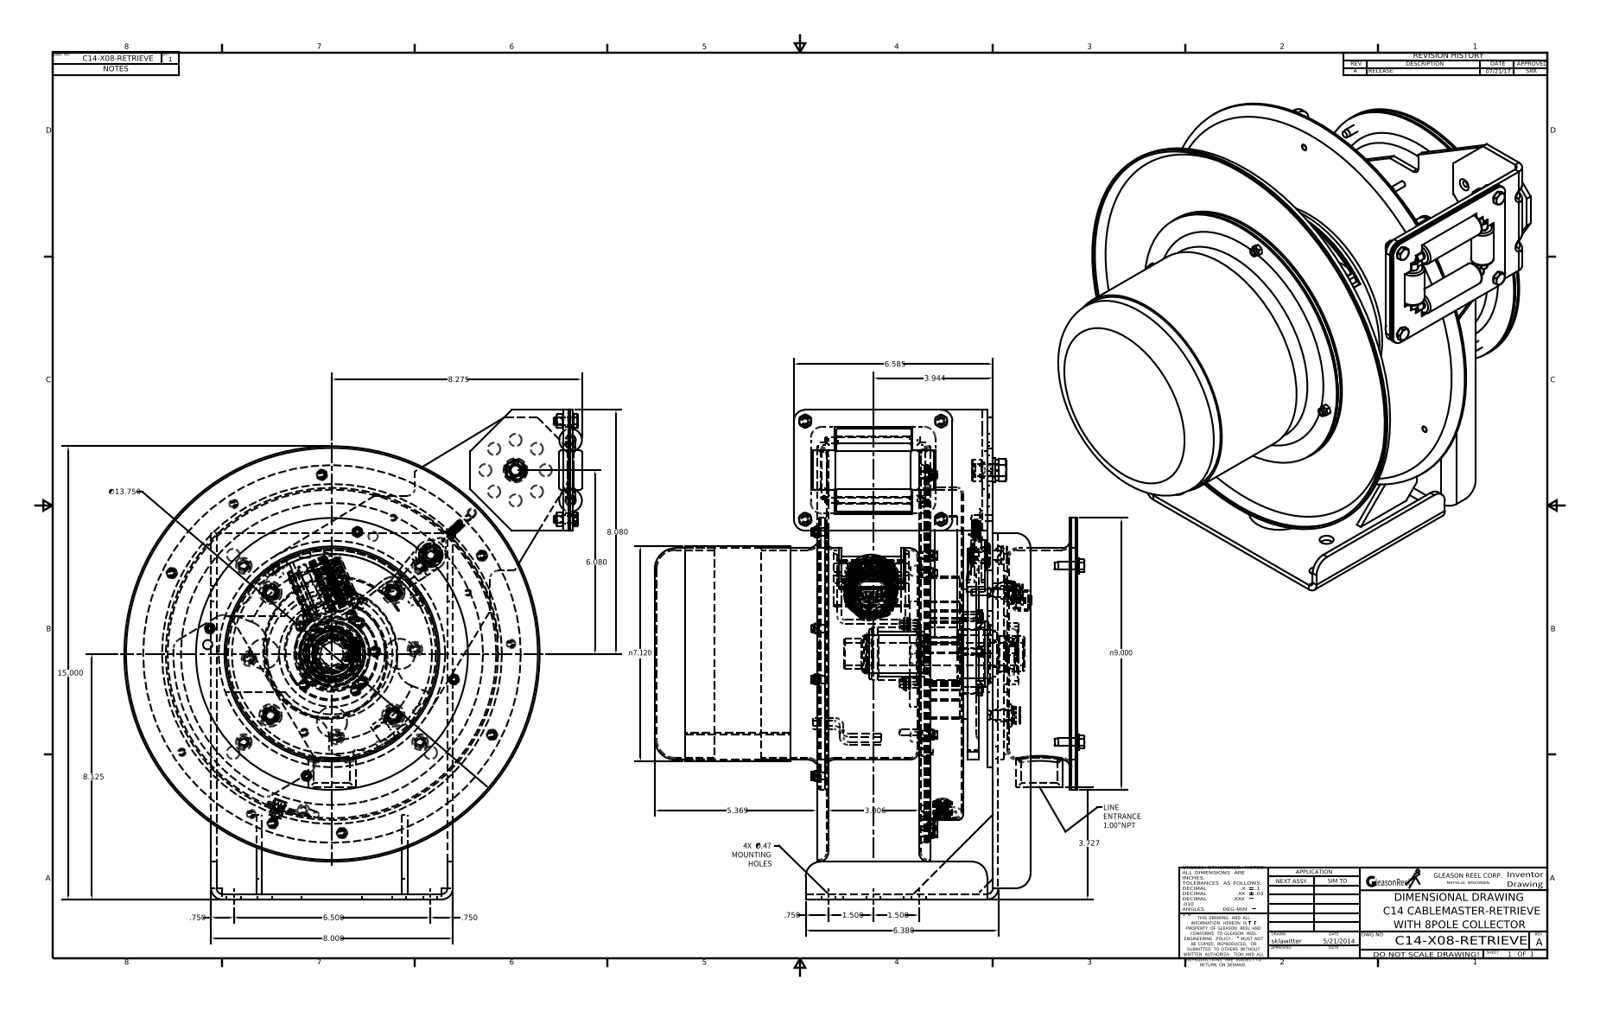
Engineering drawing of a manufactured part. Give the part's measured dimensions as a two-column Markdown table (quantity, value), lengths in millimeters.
| quantity | value |
| --- | --- |
| part name | C14-X08-RETRIEVE (SW) |
| STEP written by | Autodesk Inventor 2016 (AUTOMOTIVE_DESIGN) |
| units | millimeters |
| bodies | 159 solids, 3183 faces (1260 planar, 1033 cylindrical, 890 other) |
| overall size | 411.61 × 384.81 × 361.3 |
| volume | 2 733 000 mm³ |
| surface area | 2 334 000 mm² |
| round holes (diameter × count) | 6.35 × 26, 5 × 24, 4.13 × 19, 10.31 × 13, 5.56 × 12, 5.41 × 8, 10.67 × 8, 11.94 × 6, 25.4 × 6, 4.92 × 5, 7.14 × 5, 7.98 × 5 |
| round bosses / shafts (diameter × count) | 5 × 24, 6.8 × 11, 10 × 7, 6 × 6, 12.7 × 5, 11.6 × 5, 8 × 5, 19.05 × 4 |
| partial cylindrical surfaces (radius × count) | 0.76 × 67, 0.24 × 64, 0.38 × 58, 1.98 × 18, 0.16 × 16, 1.52 × 12, 6.35 × 8, 9.53 × 8 |
| main face-to-face distances | 1.52, 3.17, 6.19, 30.93, 126.76, 4.69, 1.5, 4.67, 4.54, 84.04 |
| hole center spacings | 19.44, 25.4, 31.75, 35.92, 46.93, 51.91, 51.93, 76 |
